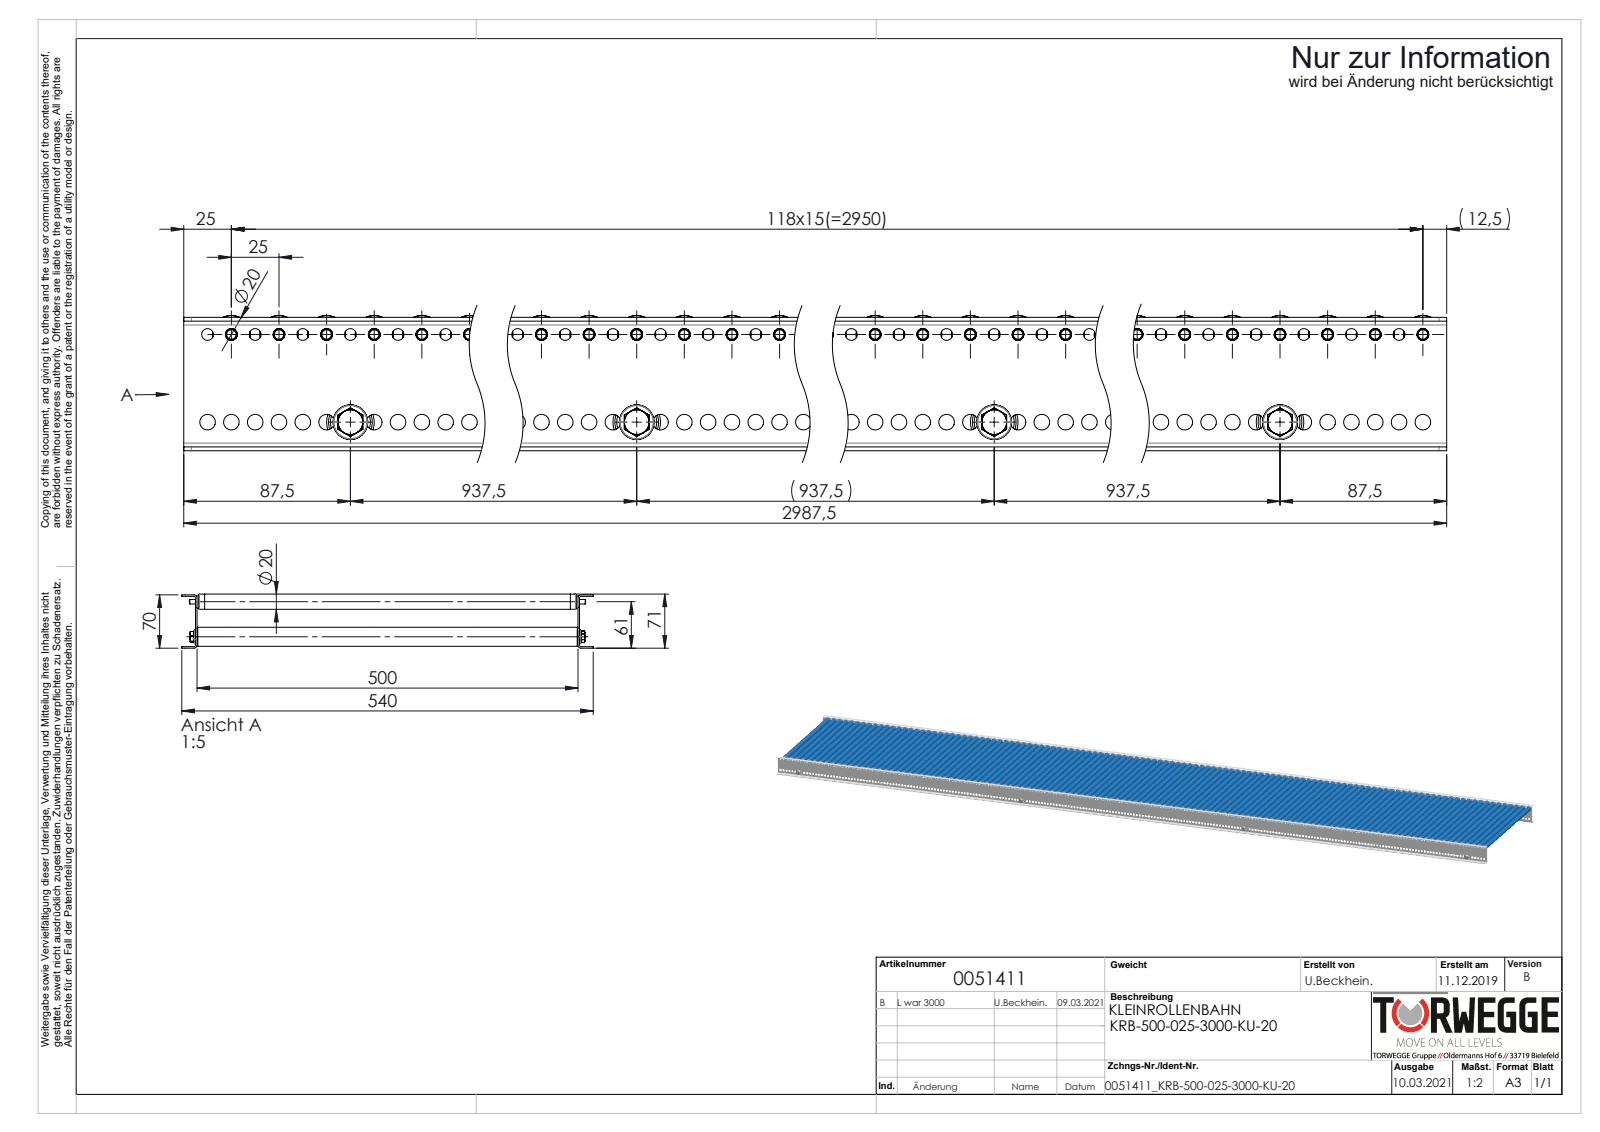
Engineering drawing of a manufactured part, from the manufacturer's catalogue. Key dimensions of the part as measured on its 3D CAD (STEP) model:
Part name (STEP PRODUCT): KUT50-20x1,5-KU-A6_FA-EL=KFG_L=500; Traversen_KFG_L500; S100994_Sperrzahnschraube_M08x16-8.8-A2K; 0039777_Achse-Ø06-FA-KFG_L=520 fr D20 (+4 more)
STEP written by: SolidWorks 2020 (AUTOMOTIVE_DESIGN)
Units: millimetres
Bodies: 736 solids, 31448 faces (10438 planar, 11758 cylindrical, 9252 other)
Overall size (bounding box): 2987.5 × 540 × 71
Volume: 9 049 000 mm³ · Surface area: 10 390 000 mm²
Round holes (diameter × count): ⌀6.2 ×238, ⌀8.2 ×238, ⌀6.1 ×119, ⌀12.4 ×119, ⌀13.2 ×119, ⌀14.6 ×119, ⌀16.2 ×119, ⌀17 ×119, ⌀17.2 ×119, ⌀6.8 ×4, ⌀21 ×4
Round bosses / shafts (diameter × count): ⌀20 ×119, ⌀19.9 ×119, ⌀17.1 ×119, ⌀16.8 ×119, ⌀16.5 ×119, ⌀11.4 ×119, ⌀11.1 ×119, ⌀10.2 ×119
Partial cylindrical surfaces — rounded edges, fillets, slot ends (radius × count): R4.05 ×119, R4 ×8, R2 ×4
Main face-to-face distances: 2, 502, 68, 500, 504, 70, 66, 492, 10, 12
Hole centre spacings: 12.5, 25, 37.5, 50, 62.5, 75, 87.5, 100
